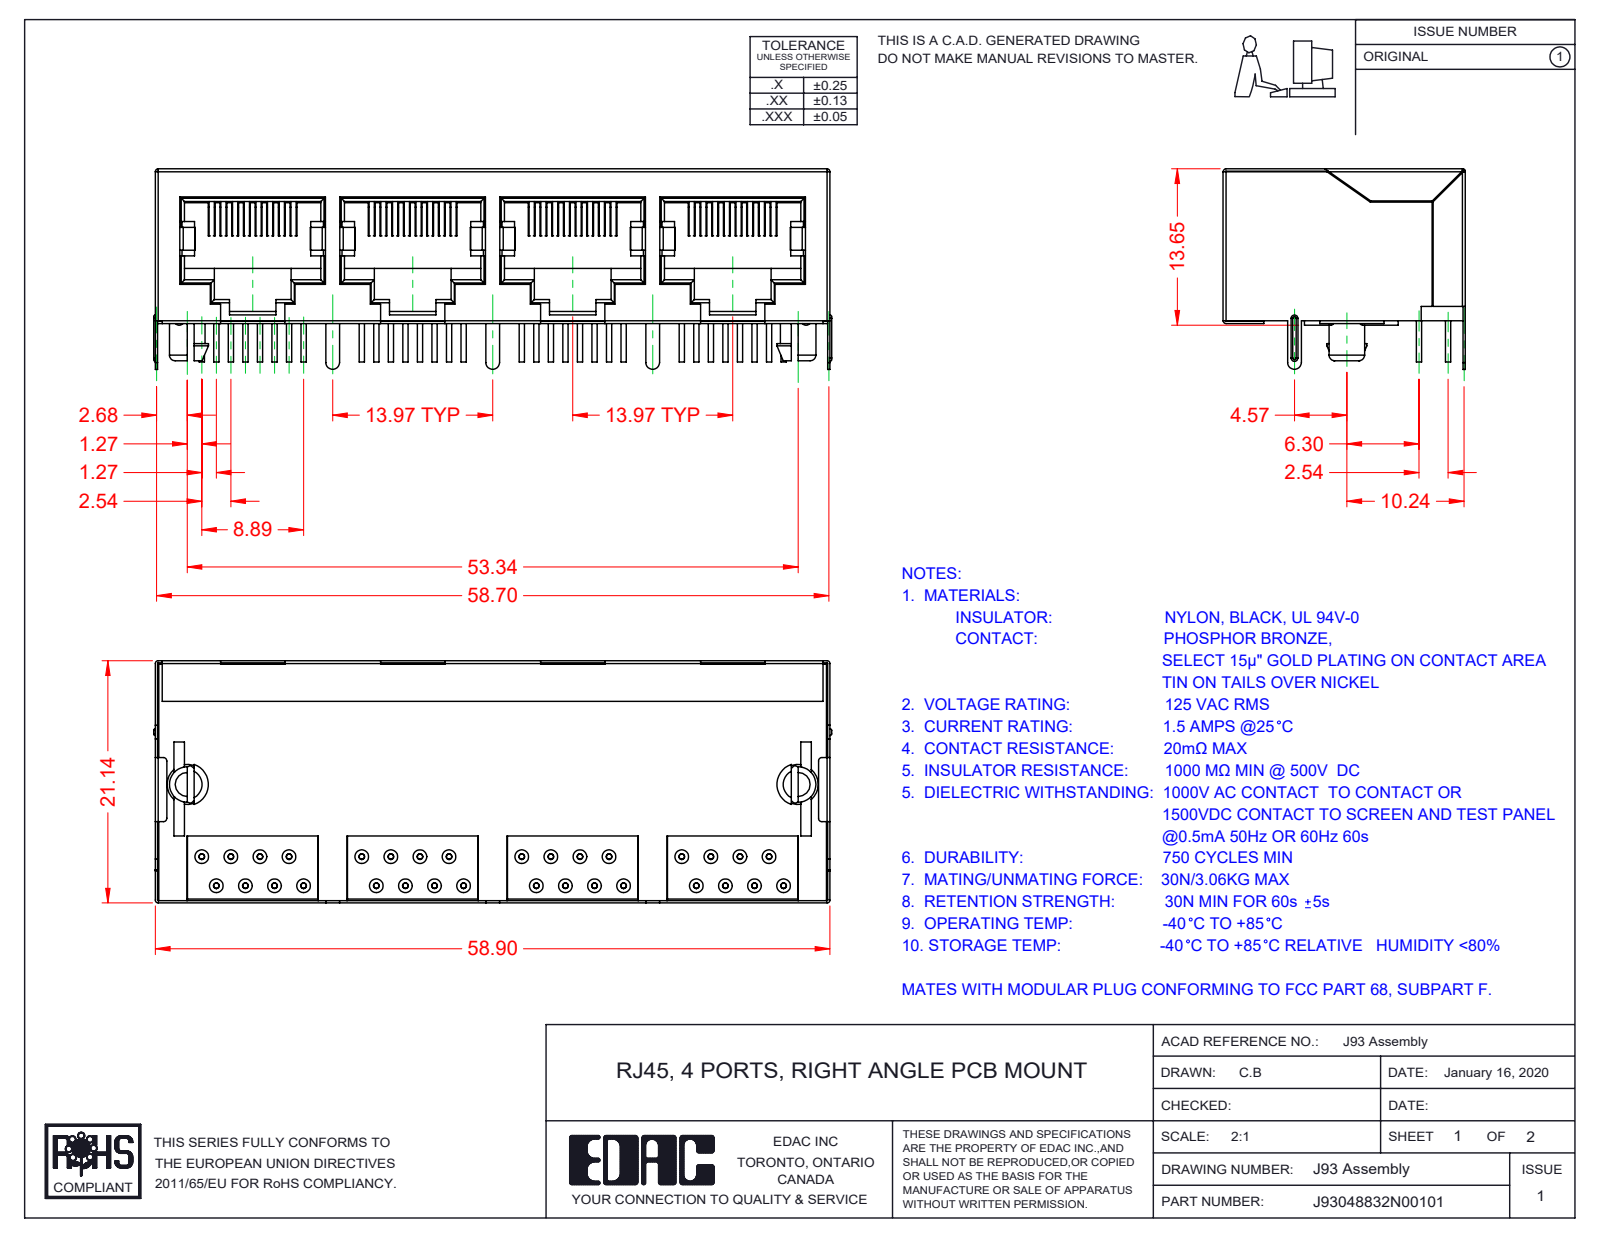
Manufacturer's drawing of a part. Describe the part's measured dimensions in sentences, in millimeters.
The part is named "93 Contact Lock; 93 Contacts; 93 Shield; RJ93048832N00101 (+1 more)". Its 3-D file was written by "SolidWorks 2016 (CONFIG_CONTROL_DESIGN)". It is 38 solids with 2070 faces: 1065 planar, 665 cylindrical and 340 other. Overall it measures 59.2 by 21.14 by 17.5 millimeters. Its volume is 9 684 cubic millimeters and its surface area 21 056 square millimeters. Round holes: 32 of diameter 0.46. Round bosses or shafts: 128 of diameter 0.46, 2 of diameter 3.1. Partial cylindrical surfaces (rounded edges, fillets, slot ends): 22 of radius 0.3, 22 of radius 0.5, 16 of radius 0.19, 11 of radius 0.25, 4 of radius 0.15, 4 of radius 0.6, 2 of radius 0.4, 2 of radius 0.46. The main face-to-face distances are 0.8, 12.25, 12.2, 1, 0.75, 13.25, 13.05, 1.05, 0.85, 13. The hole center spacings are 2.84, 2.54, 13.97, 15.45, 12.95, 4.58, 16.51, 11.43.
